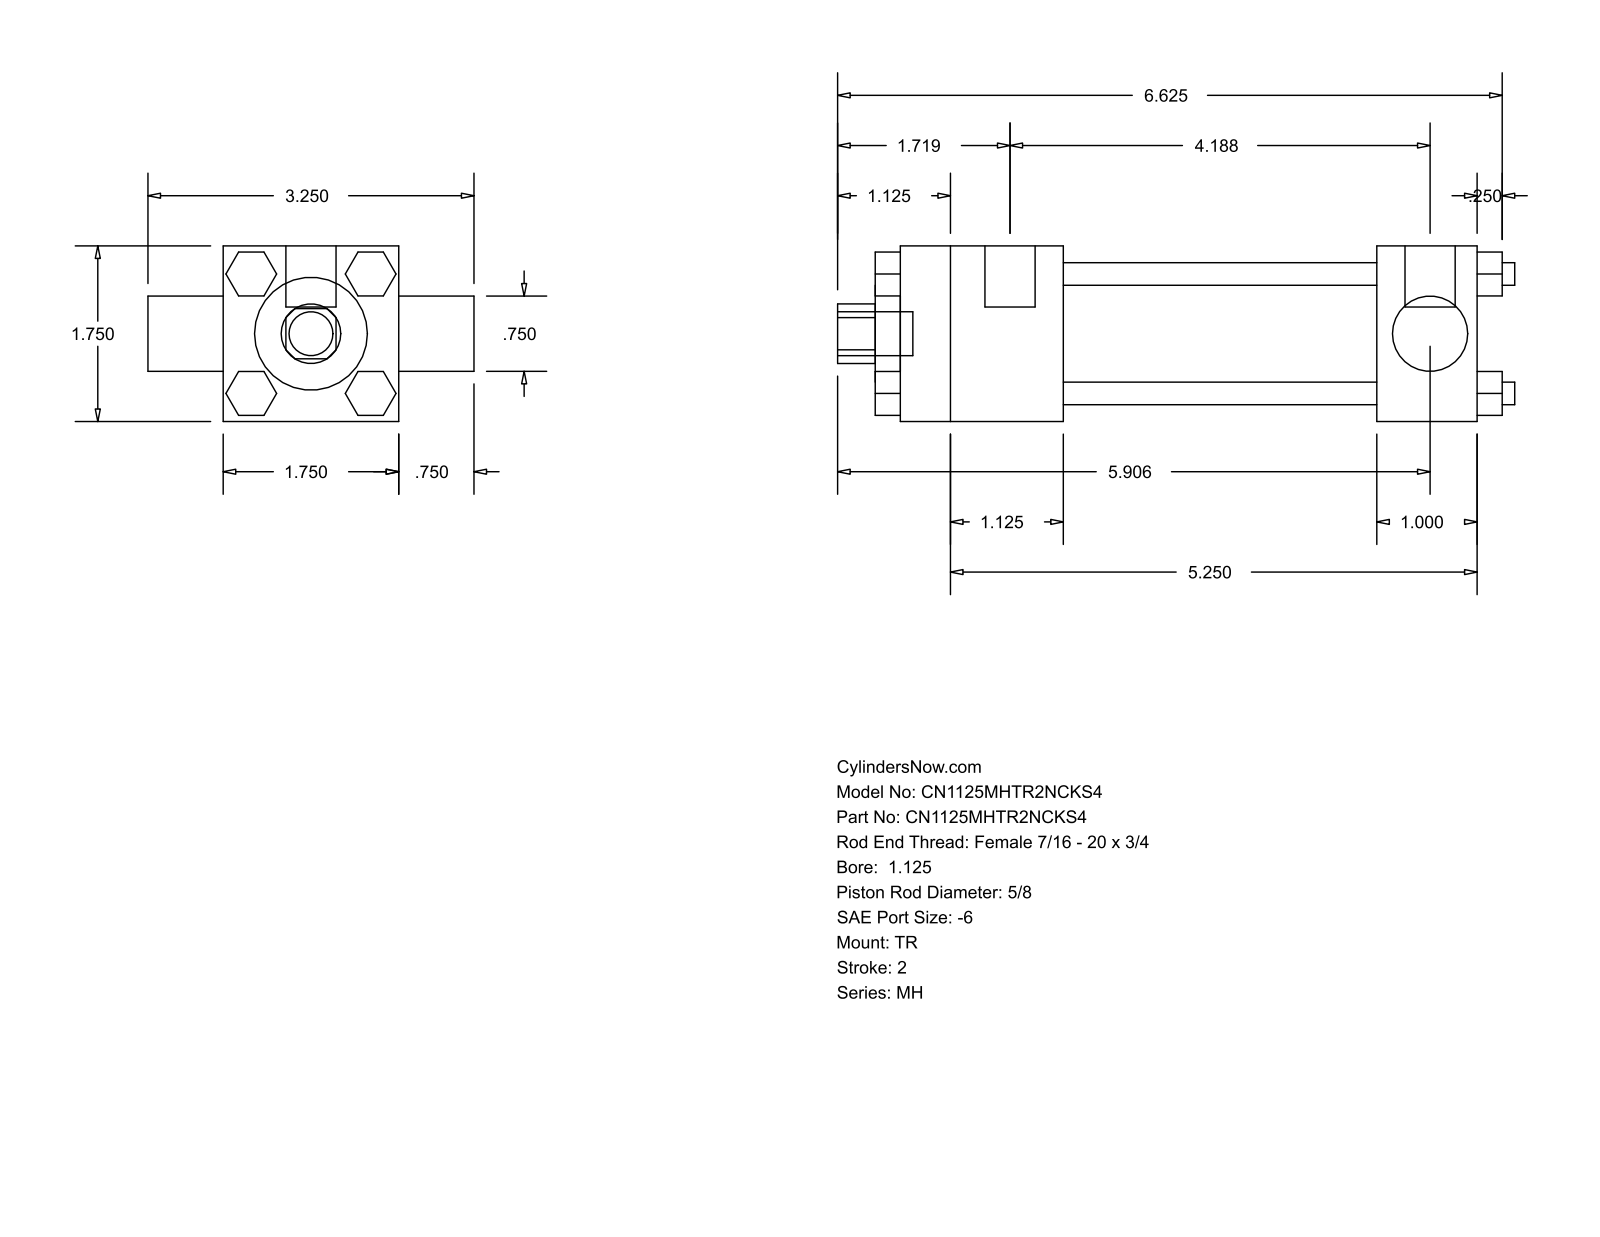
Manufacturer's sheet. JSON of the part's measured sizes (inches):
{"part_name": "MH_TR__0112_0.625", "step_written_by": "GSSL Pune (CONFIG_CONTROL_DESIGN)", "units": "inches", "bodies": {"solids": 0, "faces": 120, "planar": 92, "cylindrical": 28, "other": 0}, "overall_size": [6.75, 3.25, 1.75], "round_holes": [[0.625, 1], [0.75, 1], [1.125, 1], [1.375, 1]], "round_bosses_or_shafts": [[0.225, 4], [0.219, 3], [0.5, 2], [0.437, 1]], "partial_cylinders_radius": [[0.297, 1]], "face_to_face_distances": [1.75, 6, 0.25, 0.437, 3.125, 4.125, 1, 1.625, 4.75, 5.75]}
